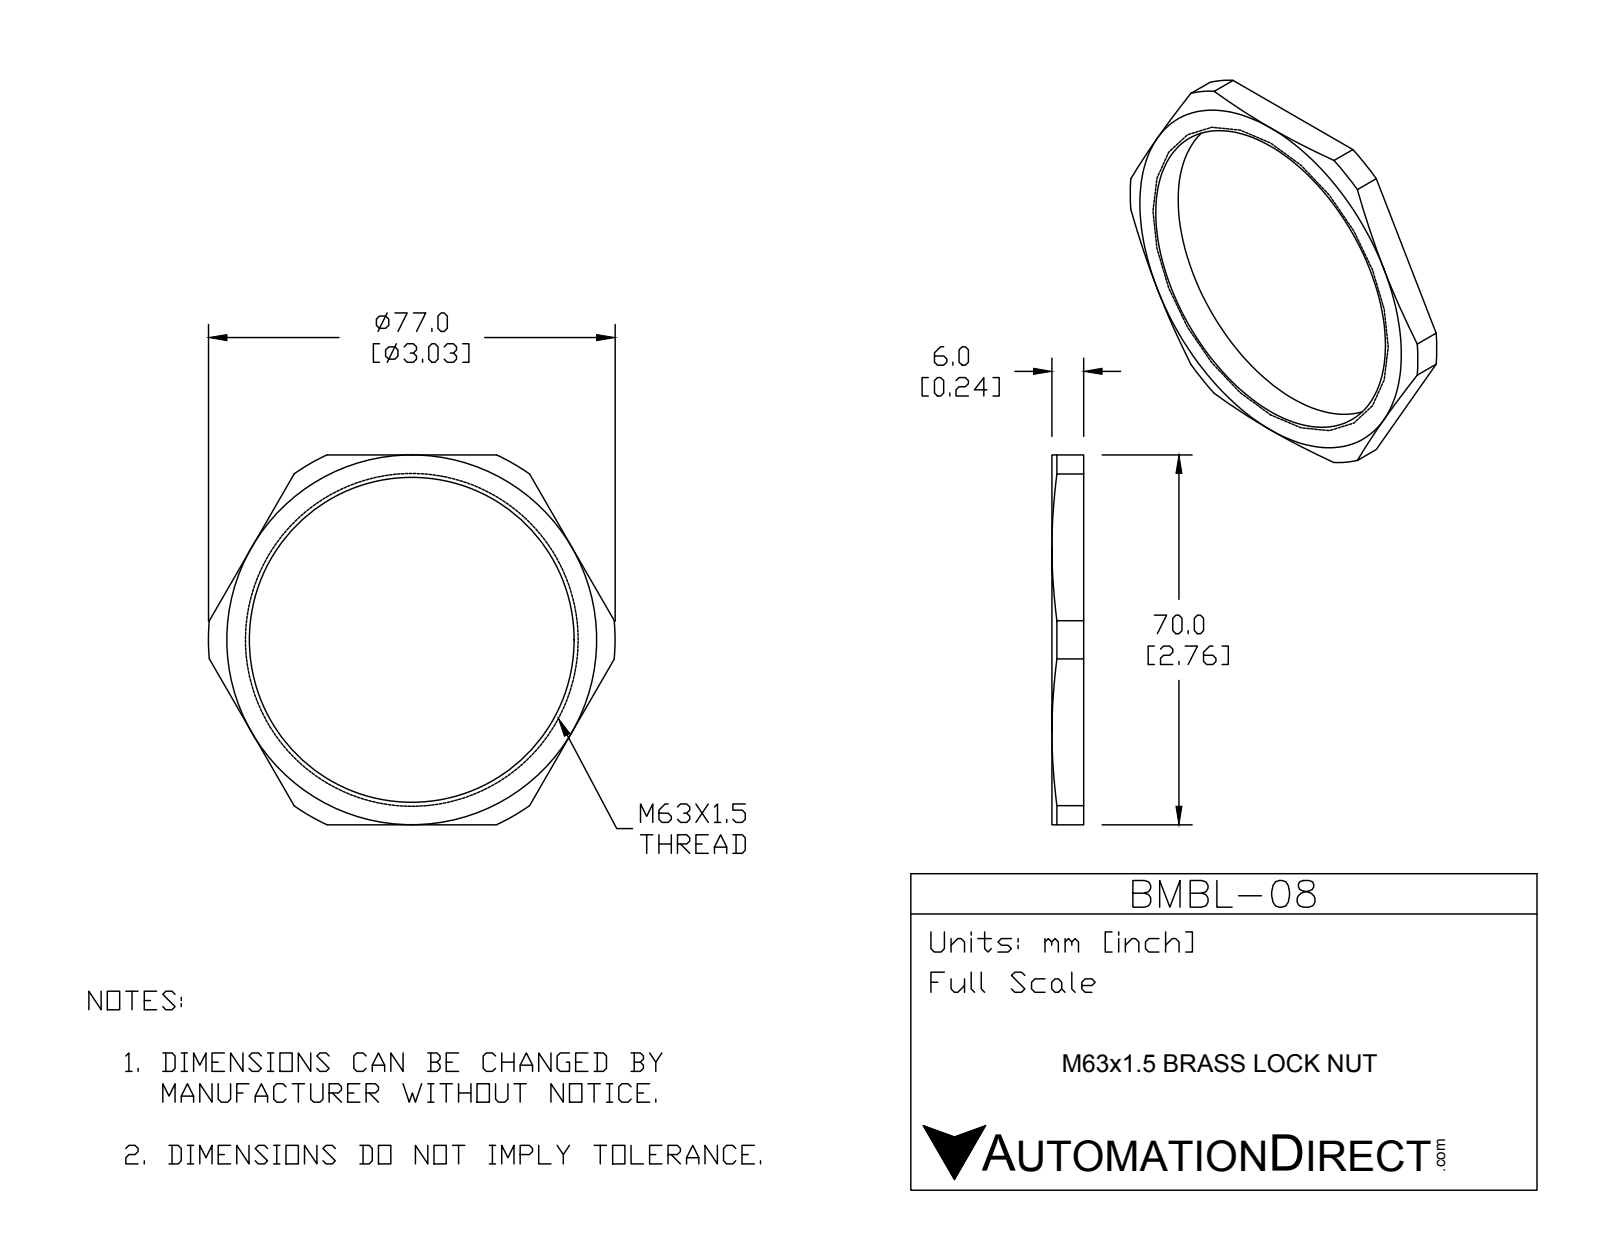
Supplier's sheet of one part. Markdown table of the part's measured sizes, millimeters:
| quantity | value |
| --- | --- |
| part name | BMBL-08 |
| STEP written by | SolidWorks 2015 (CONFIG_CONTROL_DESIGN) |
| units | millimeters |
| bodies | 1 solid, 23 faces (8 planar, 9 cylindrical, 6 other) |
| overall size | 77 × 70 × 6 |
| volume | 7 268 mm³ |
| surface area | 4 950 mm² |
| round holes (diameter × count) | 61.5 × 1 |
| partial cylindrical surfaces (radius × count) | 38.5 × 1 |
| main face-to-face distances | 6, 70 |
